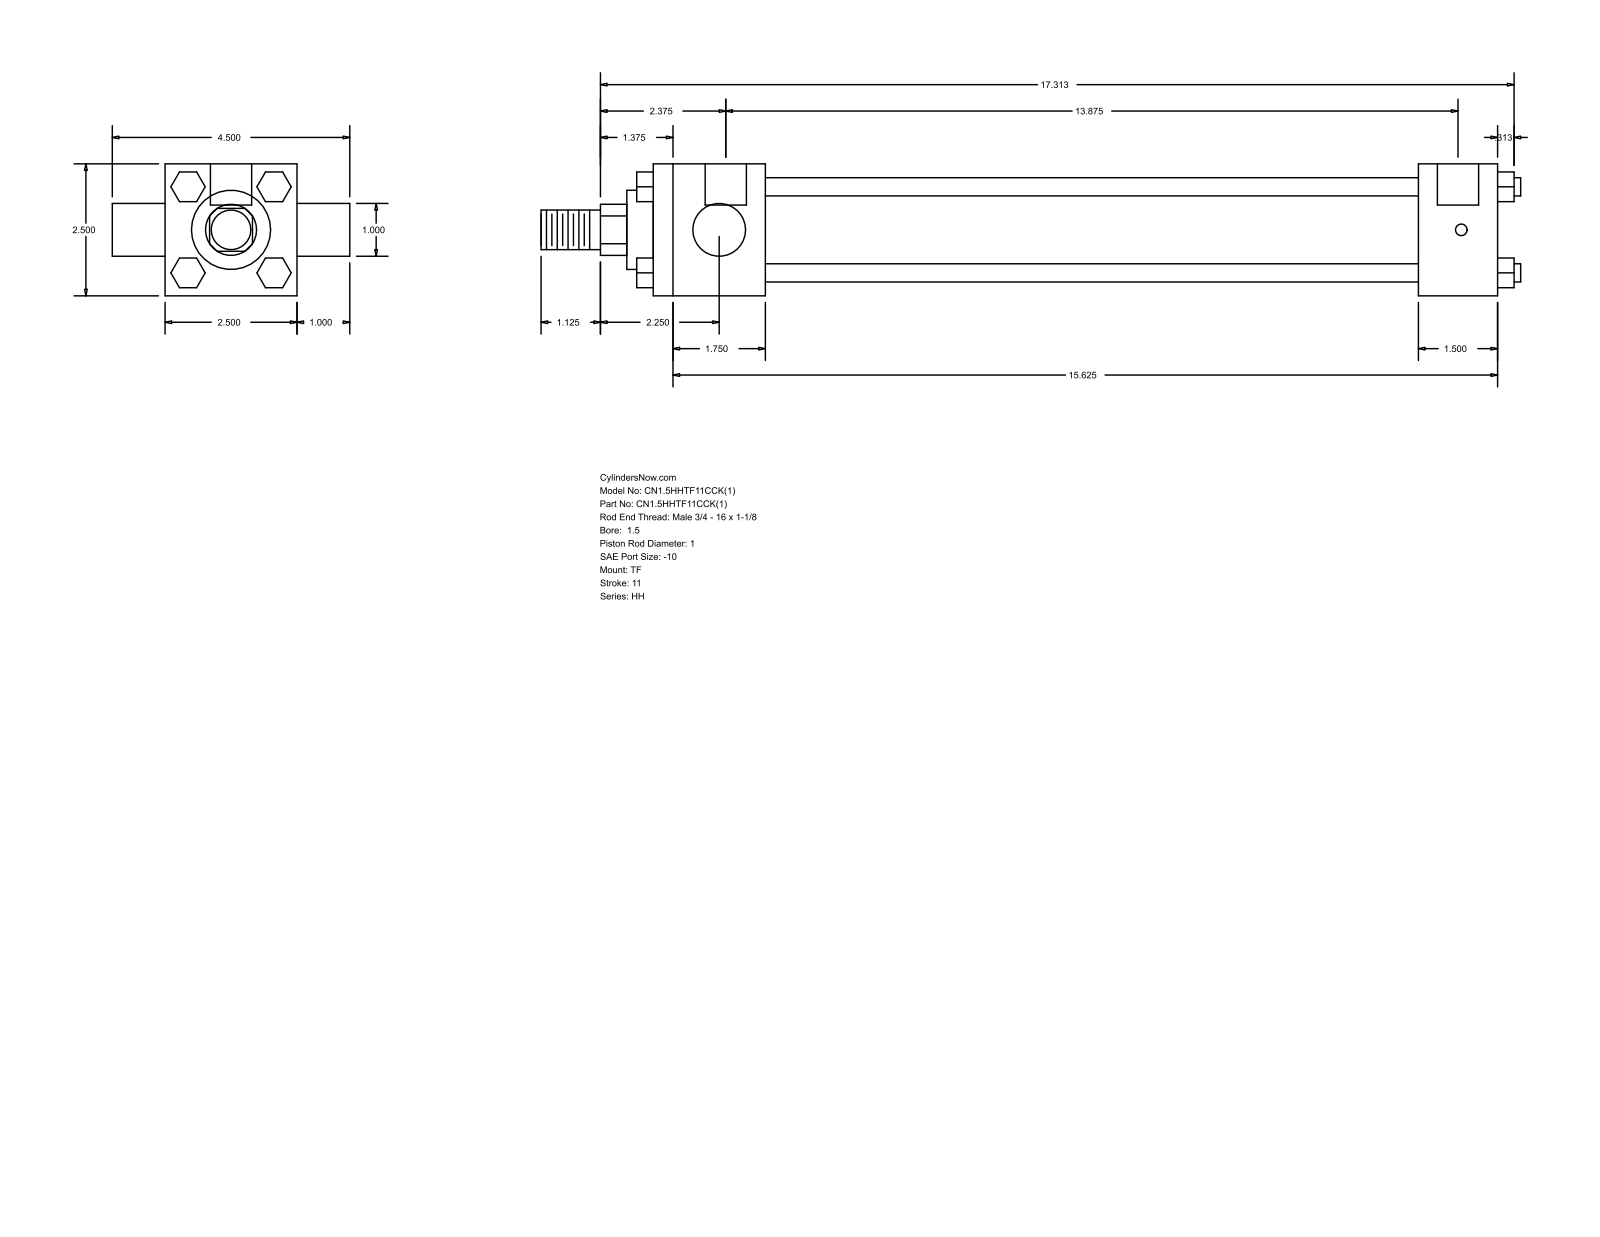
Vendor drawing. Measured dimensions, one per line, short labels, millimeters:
name: HH_TF__0150_1
written by: GSSL Pune (CONFIG_CONTROL_DESIGN)
unit: mm
bodies: 0 solids, 120 faces (92 planar, 28 cylindrical, 0 other)
size: 471.49 × 114.3 × 63.5
holes: 3× ⌀5.56, 2× ⌀19.84
bosses: 4× ⌀8.76, 2× ⌀25.4, 1× ⌀44.45, 1× ⌀38.1, 1× ⌀19.05
rounds: 1× R12.29
face distances: 63.5, 38.1, 352.42, 314.32, 53.98, 368.3, 406.4, 25.4, 20.7, 14.29
hole spacings: 1.59, 354.01, 352.42, 355.6
